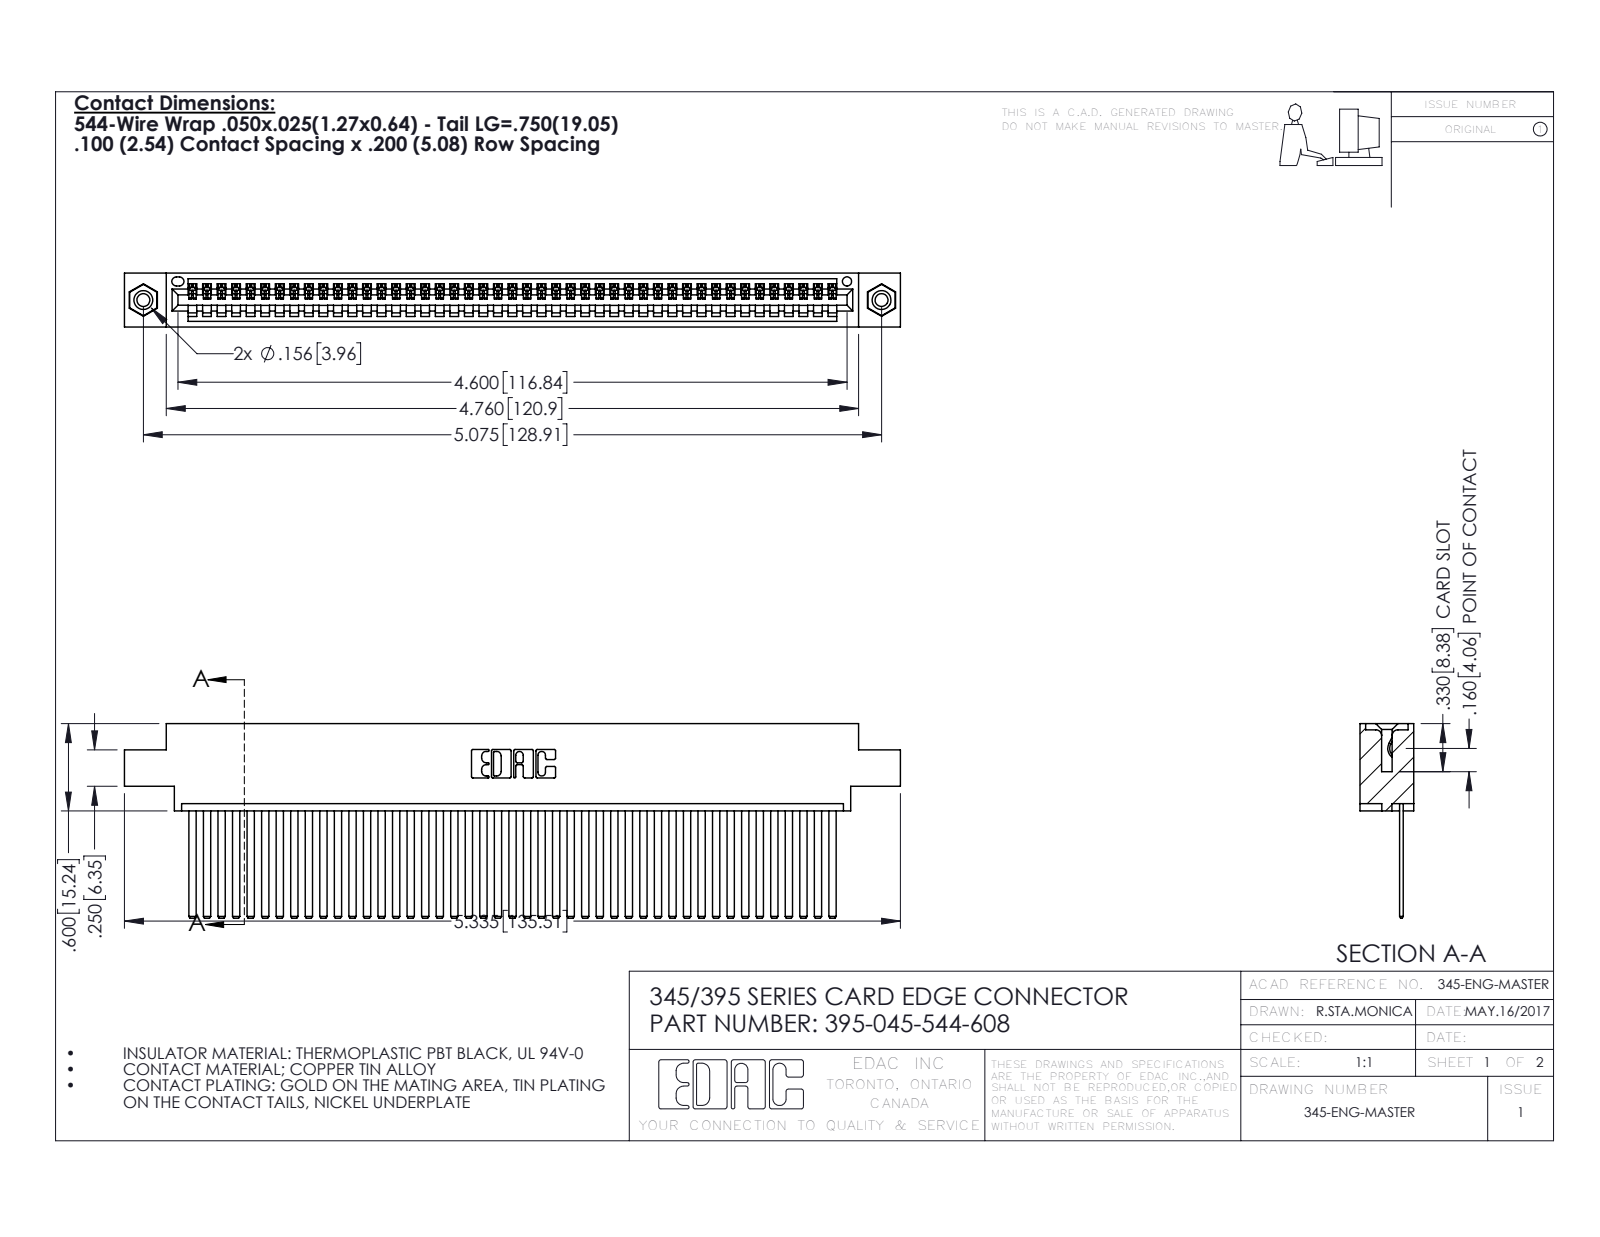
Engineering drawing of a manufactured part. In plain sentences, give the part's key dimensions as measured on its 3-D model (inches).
The part is named "395-045-544-608; 345-292-001_345-293-144; 345-250-001_345-250-003-102; 345 Part_0.170 Offset - 0.156 Dia-TI". Its 3-D file was written by "SolidWorks 2016 (CONFIG_CONTROL_DESIGN)". It is 48 solids with 2530 faces: 1736 planar, 778 cylindrical and 16 other. Overall it measures 5.335 by 1.337 by 0.37 inches. Its volume is 0.811 cubic inches and its surface area 30.1 square inches. Round holes: 2 of diameter 0.089, 2 of diameter 0.125, 2 of diameter 0.156, 1 of diameter 0.064. Round bosses or shafts: 2 of diameter 0.155. Partial cylindrical surfaces (rounded edges, fillets, slot ends): 90 of radius 0.006, 22 of radius 0.01, 6 of radius 0.007, 6 of radius 0.031, 3 of radius 0.026, 2 of radius 0.031, 2 of radius 0.04, 1 of radius 0.014. The main face-to-face distances are 0.072, 0.298, 0.025, 0.098, 0.272, 0.37, 0.2, 0.225, 0.175, 0.149. The hole center spacings are 0.27, 4.839, 5.075.
